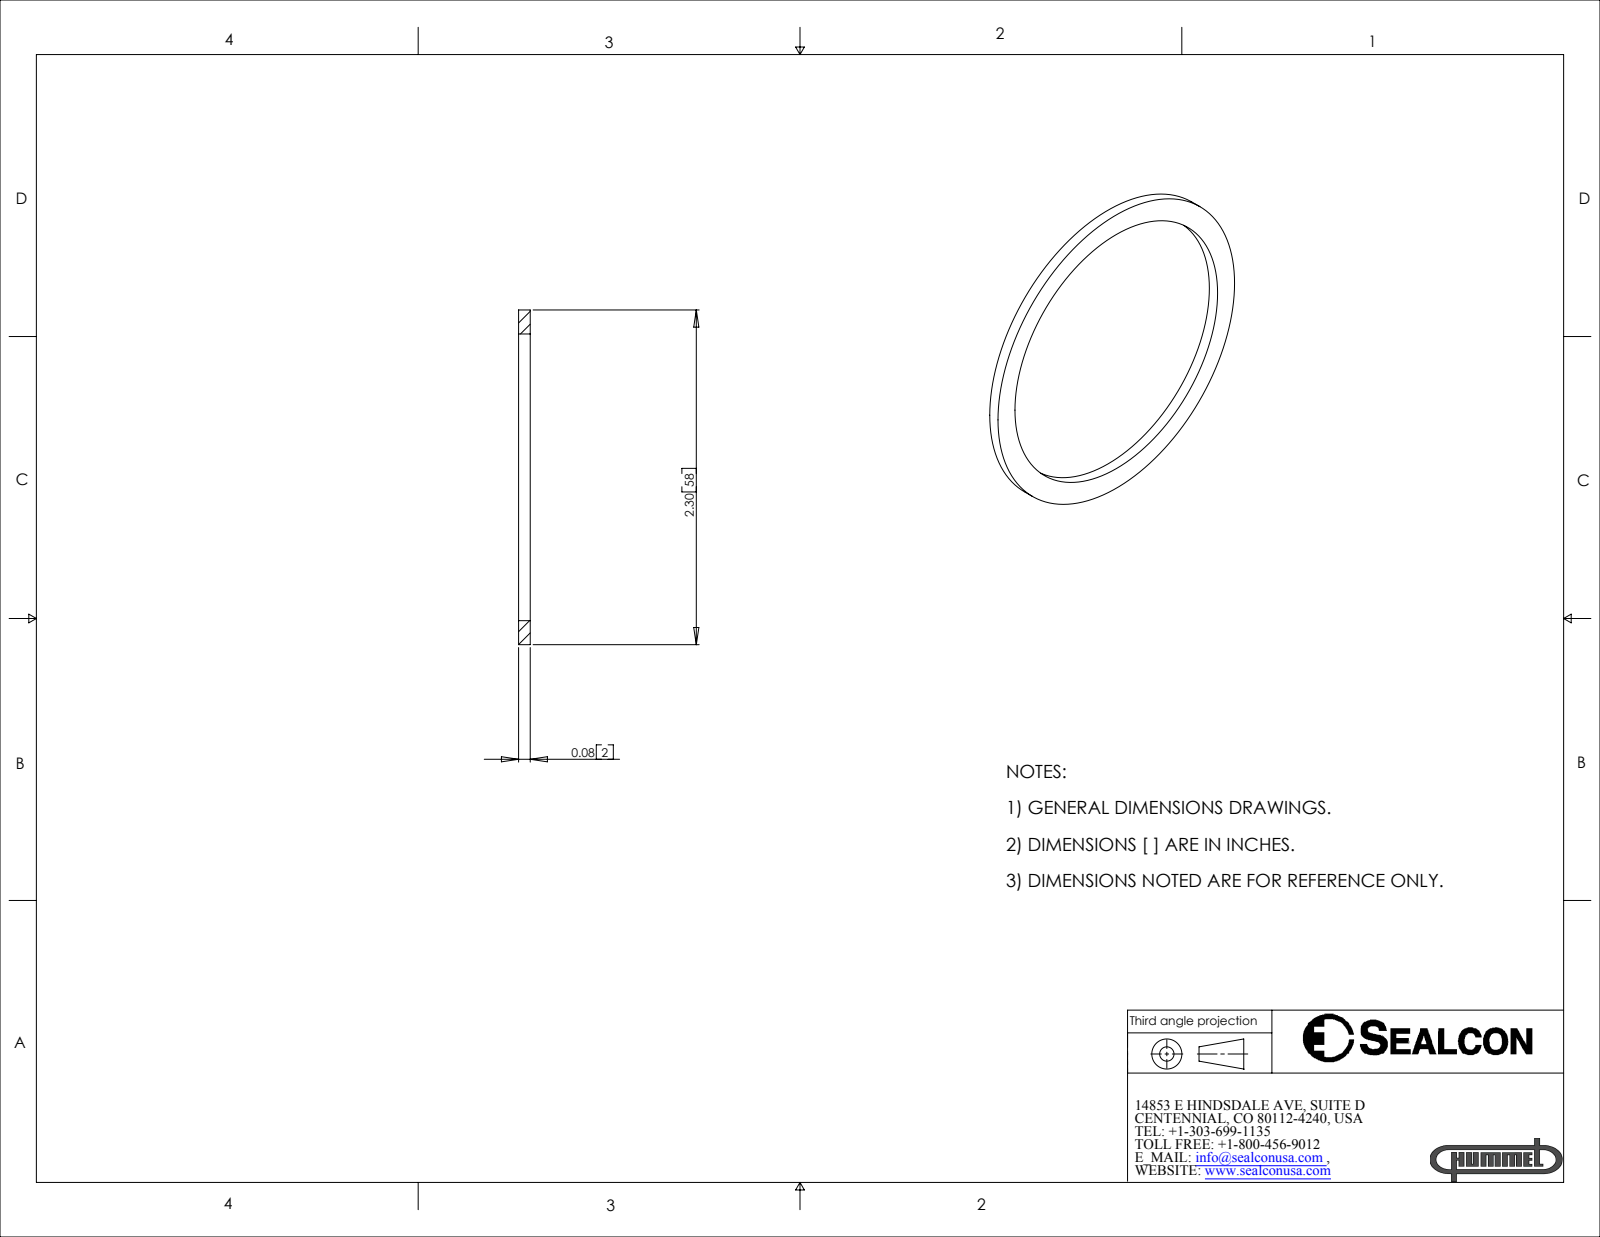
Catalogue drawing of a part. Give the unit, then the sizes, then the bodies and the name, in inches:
Units: inches
Overall size (bounding box): 2.3 × 2.3 × 0.08
Round holes (diameter × count): ⌀1.97 ×1
Round bosses / shafts (diameter × count): ⌀2.3 ×1
Main face-to-face distances: 0.08
Volume: 0.089 in³ · Surface area: 3.287 in²
Bodies: 1 solid, 6 faces (2 planar, 4 cylindrical, 0 other)
Part name (STEP PRODUCT): SM-50-VT
STEP written by: SolidWorks 2007 (CONFIG_CONTROL_DESIGN)
